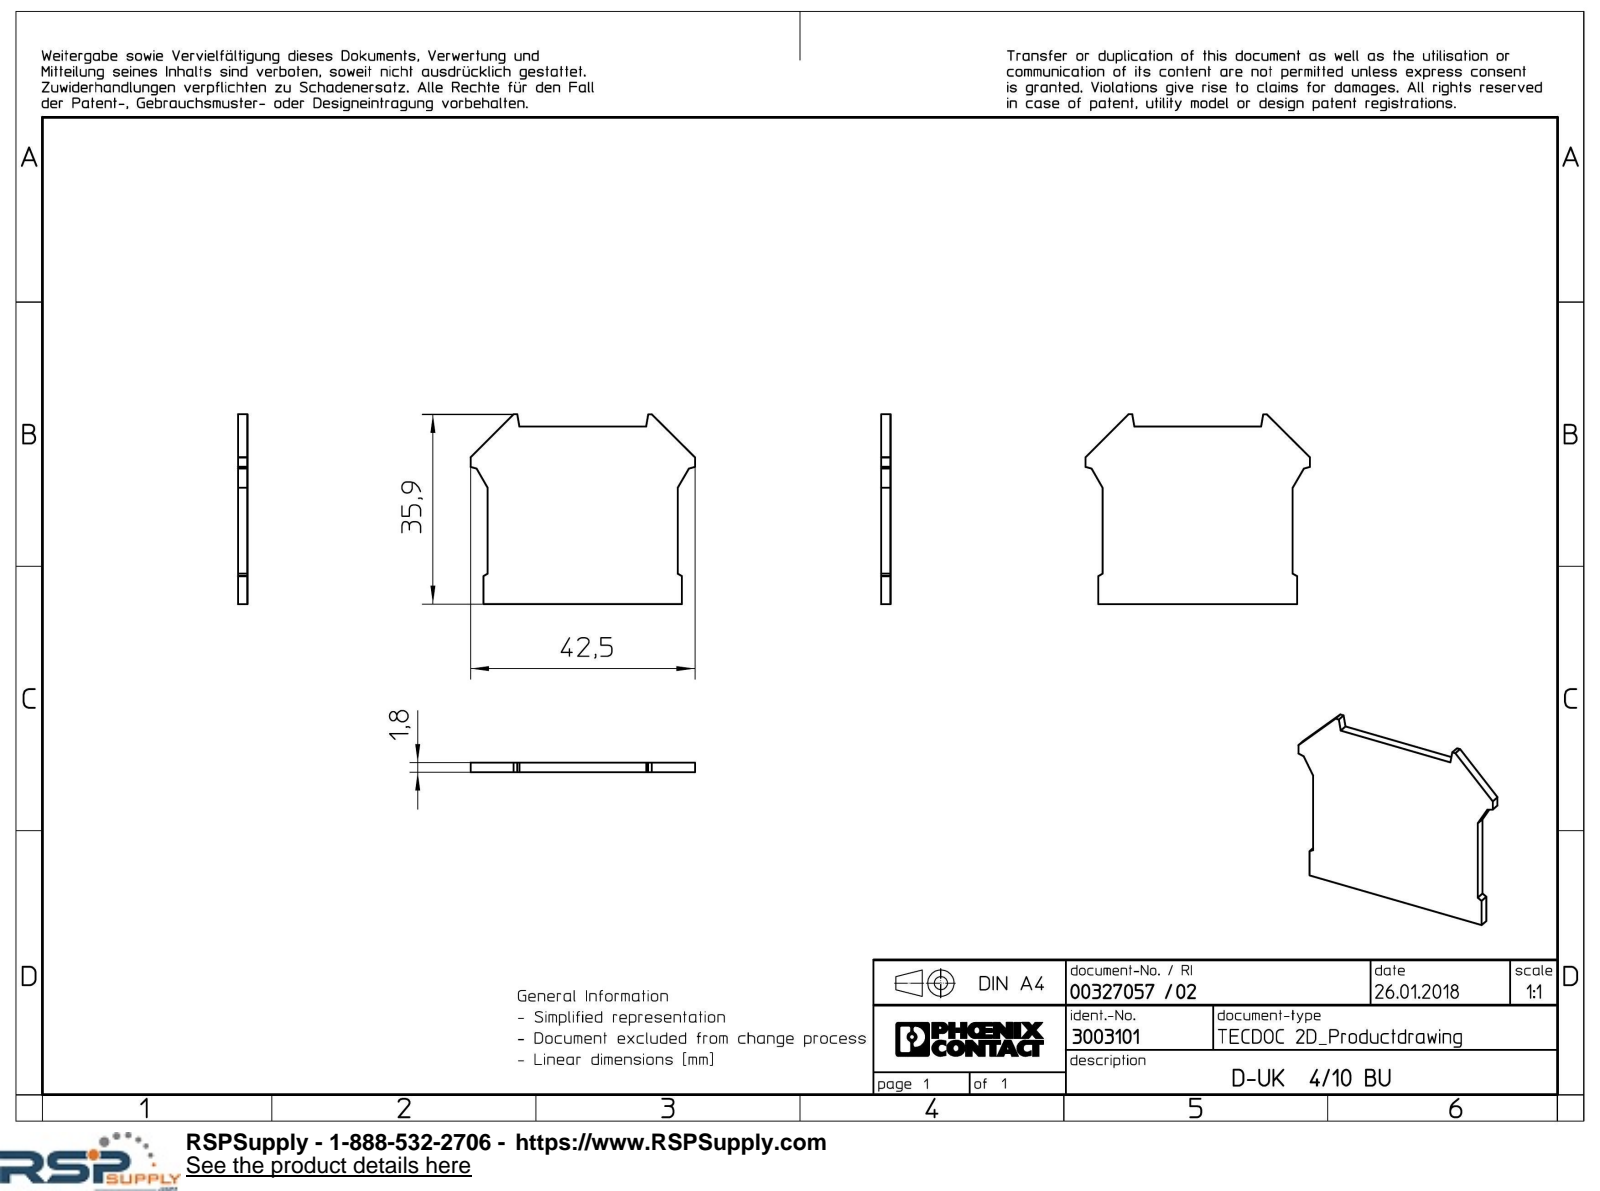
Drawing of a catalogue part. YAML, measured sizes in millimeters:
part_name: "D-UK_4_10_BU-select"
step_written_by: "Creo Elements/Direct Modeling 18.1I 14-Aug-2016 (C) Parametric Technology GmbH (AUTOMOTIVE_DESIGN)"
units: millimeters
bodies: {solids: 1, faces: 22, planar: 22, cylindrical: 0, other: 0}
overall_size: [42.5, 35.9, 1.8]
volume: 2255
surface_area: 2775
face_to_face_distances: [1.8, 33.6, 36, 0.8, 36.8, 37.6, 2.45, 3.25, 39.25, 40.05]
